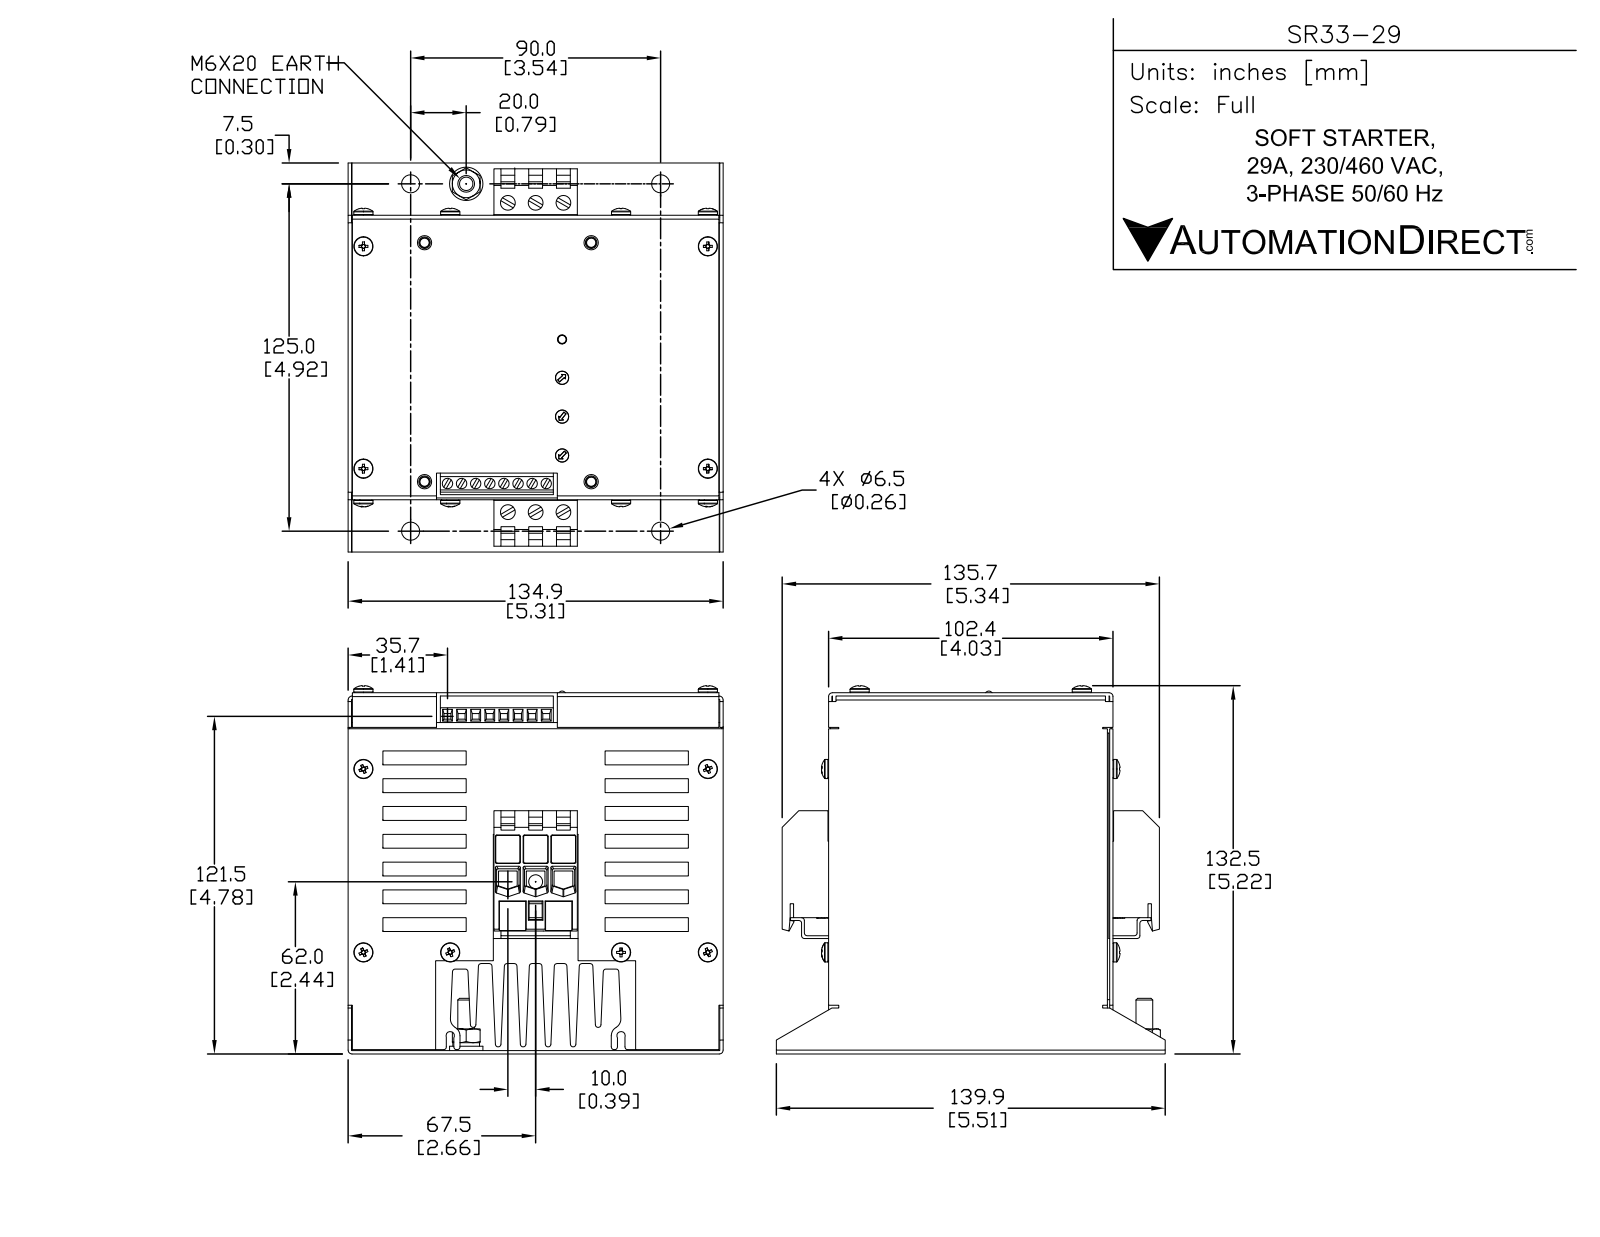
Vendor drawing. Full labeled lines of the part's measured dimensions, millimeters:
Part name (STEP PRODUCT): SR33-29
STEP written by: SolidWorks 2013 (AUTOMOTIVE_DESIGN)
Units: millimetres
Bodies: 1 solid, 980 faces (712 planar, 170 cylindrical, 98 other)
Overall size (bounding box): 139.9 × 134.9 × 132.9
Volume: 1 475 000 mm³ · Surface area: 260 135 mm²
Round holes (diameter × count): ⌀3.82 ×8, ⌀5 ×6, ⌀6.5 ×4
Round bosses / shafts (diameter × count): ⌀6.9 ×10, ⌀12 ×1, ⌀6 ×1
Partial cylindrical surfaces — rounded edges, fillets, slot ends (radius × count): R1 ×30, R0.44 ×14, R3 ×5, R2 ×4, R0.57 ×3, R0.5 ×2, R0.52 ×2, R0.52 ×2
Main face-to-face distances: 5, 10, 15, 20, 30, 25, 35, 40, 45, 50
Hole centre spacings: 10, 5, 20, 15, 35.55, 45.43, 55.35, 113.02
